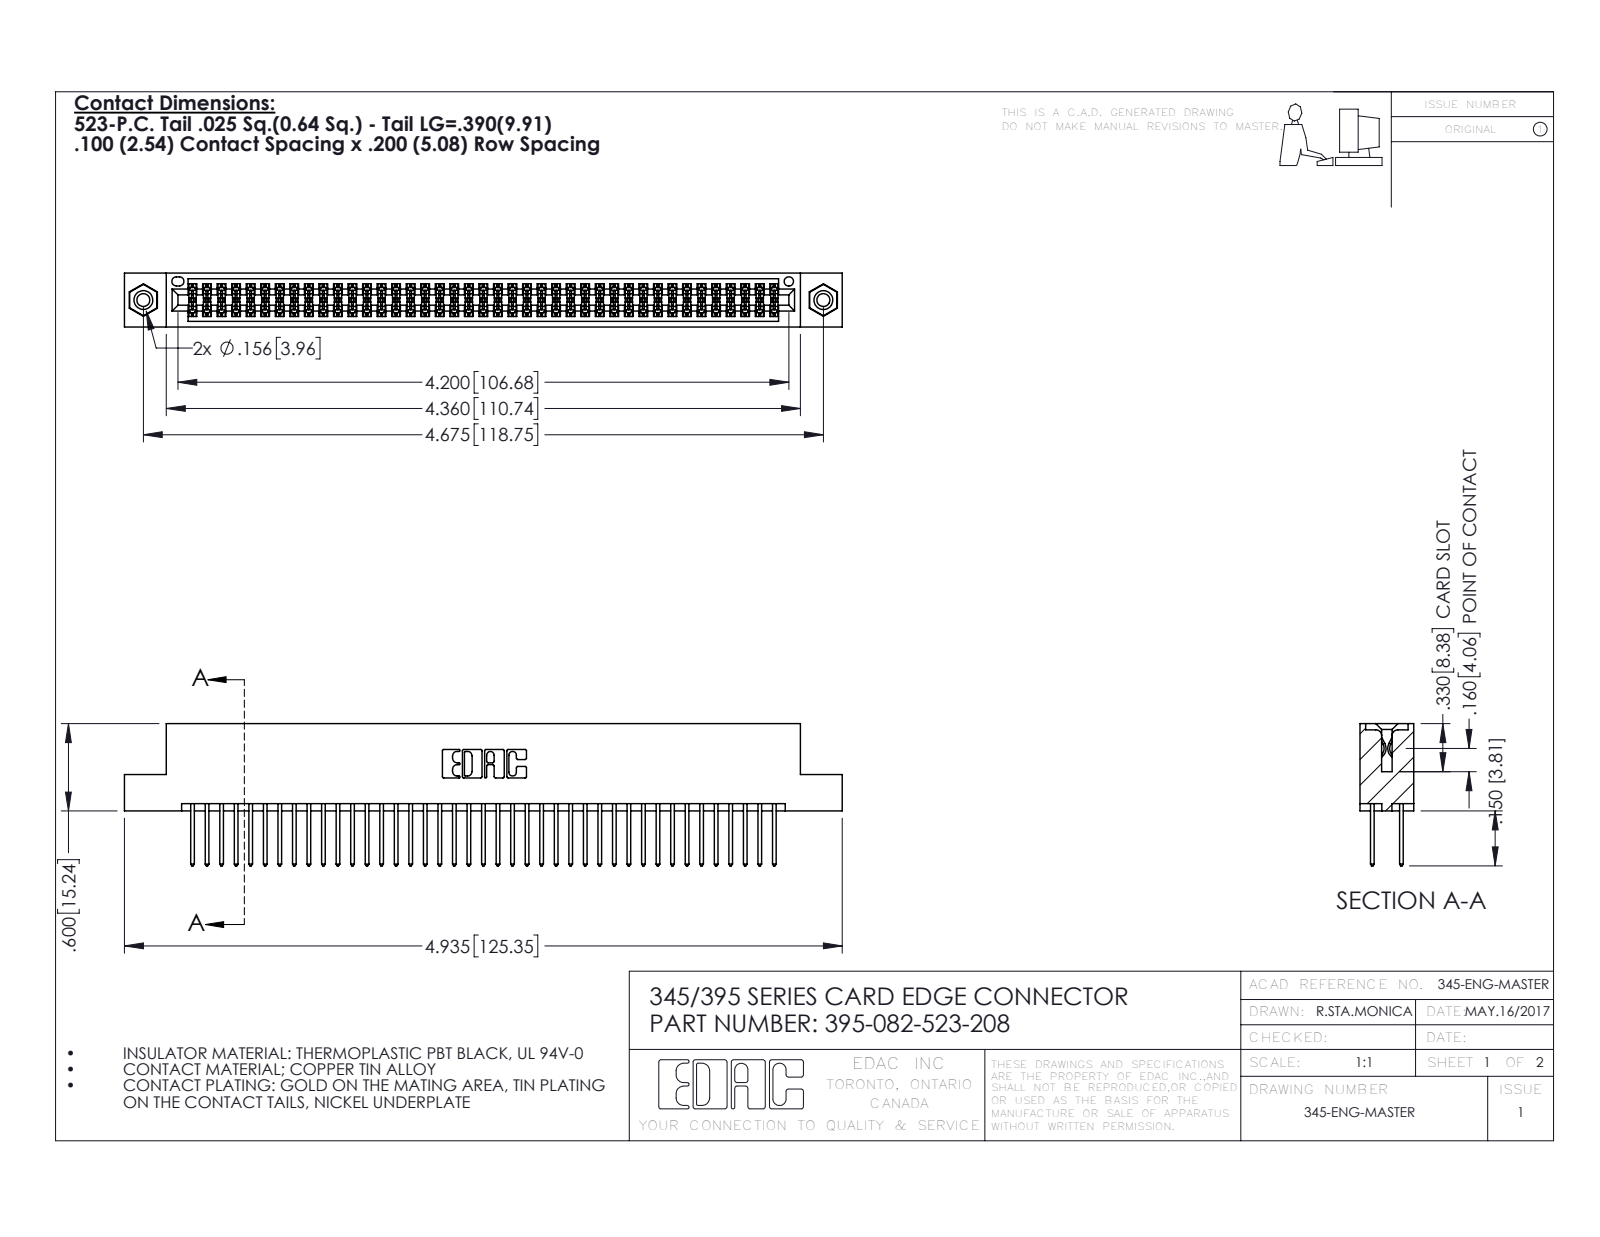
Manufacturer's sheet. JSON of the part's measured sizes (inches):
{"part_name": "345-250-001_345-250-003-102; 345 Part_Flush Mounting Lugs - 0.156 Dia-TI; 345-292-001_345-293-123; 395-082-523-208", "step_written_by": "SolidWorks 2016 (CONFIG_CONTROL_DESIGN)", "units": "inches", "bodies": {"solids": 85, "faces": 4286, "planar": 2818, "cylindrical": 1452, "other": 16}, "overall_size": [4.935, 0.977, 0.37], "volume_in3": 0.752, "surface_area_in2": 29.41, "round_holes": [[0.089, 2], [0.125, 2], [0.156, 2], [0.064, 1]], "round_bosses_or_shafts": [[0.155, 2]], "partial_cylinders_radius": [[0.006, 123], [0.01, 82], [0.01, 22], [0.007, 6], [0.031, 6], [0.026, 3], [0.014, 2], [0.019, 2]], "face_to_face_distances": [0.072, 0.298, 0.2, 0.098, 0.272, 0.025, 0.37, 0.225, 0.175, 0.149], "hole_center_spacings": [0.27, 4.439, 4.675]}
